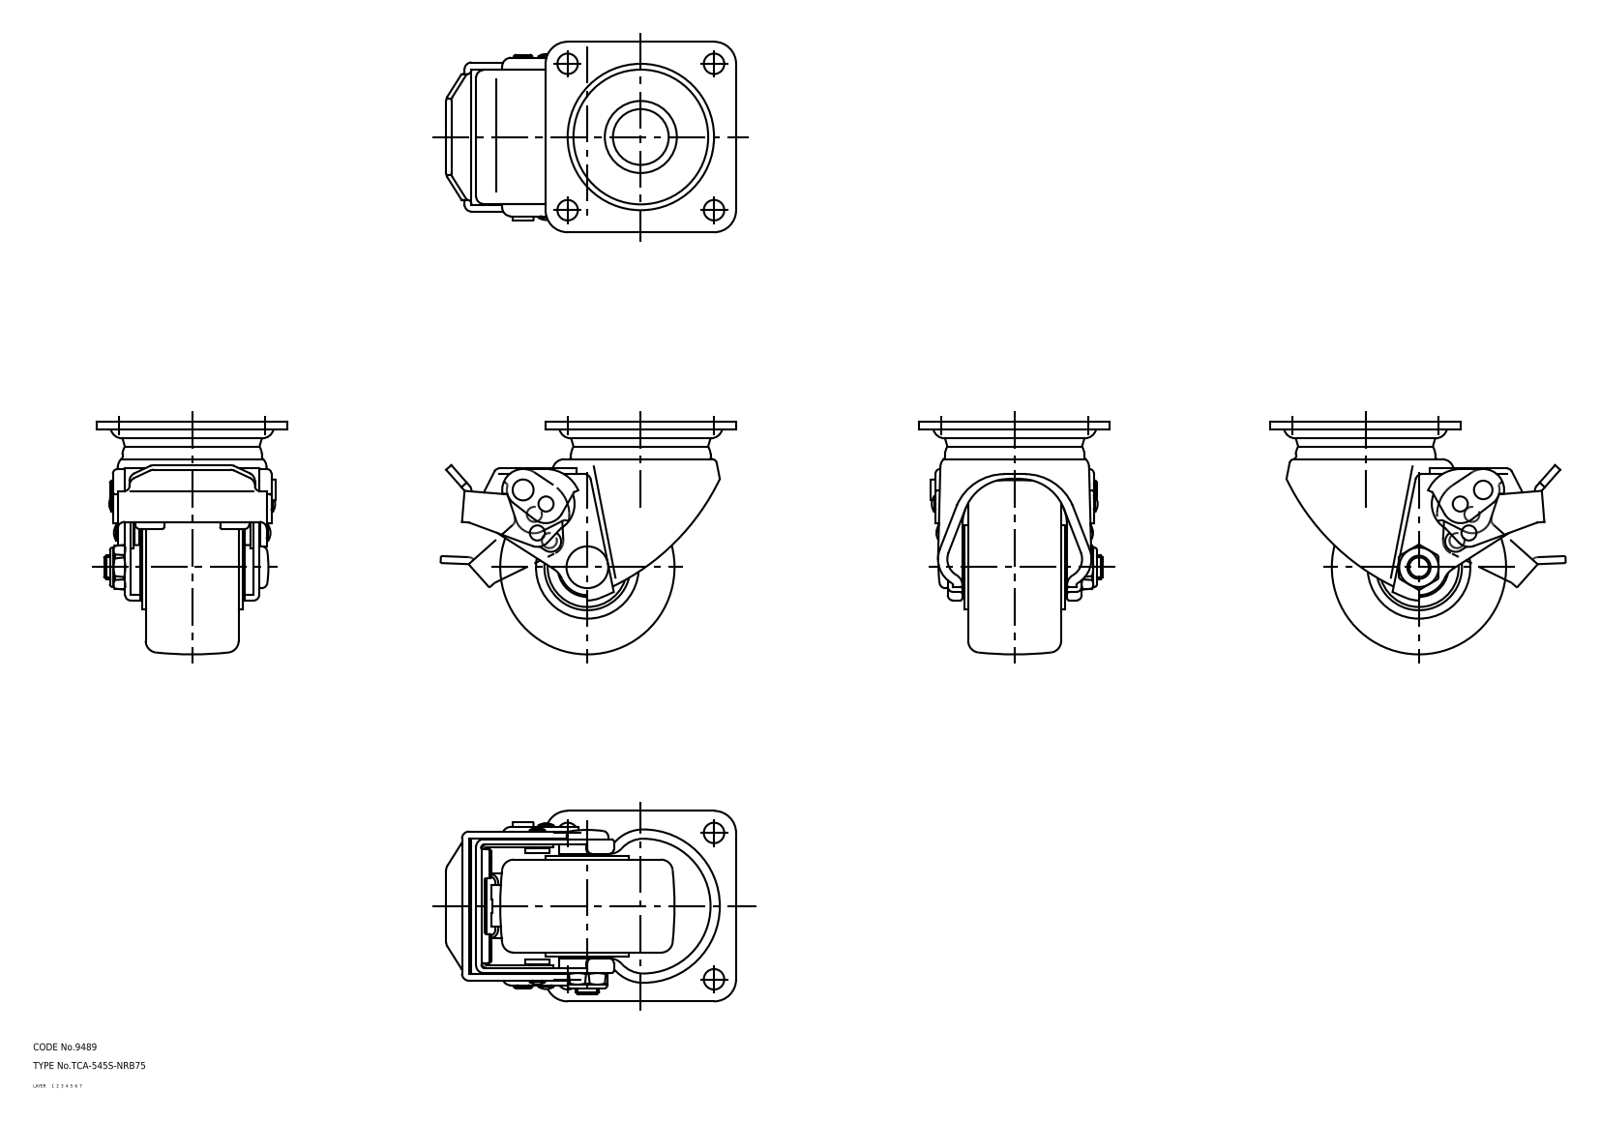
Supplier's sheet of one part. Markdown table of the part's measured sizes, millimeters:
| quantity | value |
| --- | --- |
| part name | lever; main shaft; wheel; mounting plate (+2 more) |
| STEP written by | CADfix (AUTOMOTIVE_DESIGN) |
| units | millimeters |
| bodies | 6 solids, 489 faces (0 planar, 0 cylindrical, 489 other) |
| overall size | 124.79 × 100 × 82 |
| volume | 304 103 mm³ |
| surface area | 92 539 mm² |
